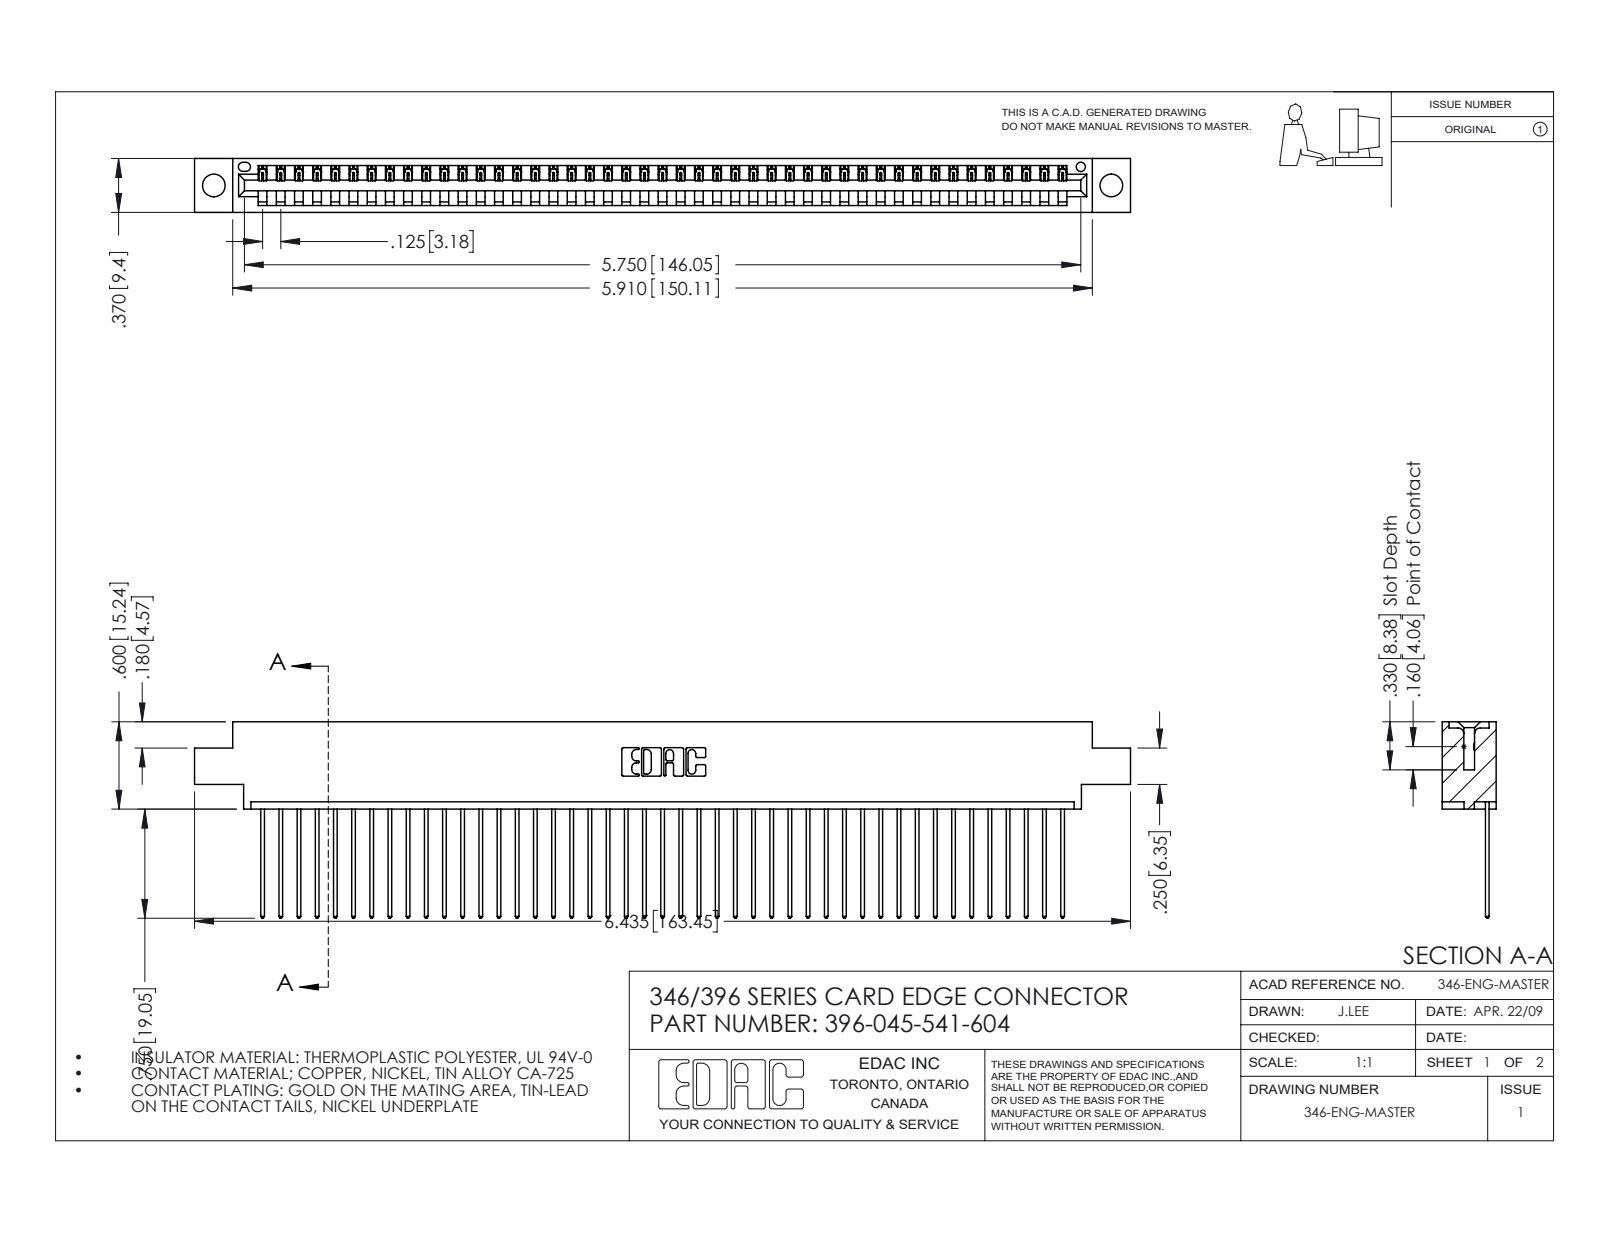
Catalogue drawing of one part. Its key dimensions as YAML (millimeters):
part_name: "345-292-001_345-293-141; 396-045-541-604; 346 Part_0.170 Offset - 0.156 Dia-TH"
step_written_by: "SolidWorks 2016 (CONFIG_CONTROL_DESIGN)"
units: millimeters
bodies: {solids: 46, faces: 2736, planar: 1880, cylindrical: 856, other: 0}
overall_size: [163.4, 34.3, 9.4]
volume: 15600
surface_area: 20350
round_holes:
  - {diameter: 4, count: 2}
  - {diameter: 1.6, count: 1}
partial_cylinders:
  - {radius: 0.2, count: 90}
  - {radius: 0.3, count: 90}
  - {radius: 0.3, count: 22}
  - {radius: 0.2, count: 6}
  - {radius: 0.8, count: 6}
  - {radius: 0.7, count: 3}
  - {radius: 0.8, count: 2}
  - {radius: 1, count: 2}
face_to_face_distances: [1.2, 8.2, 9.4, 6.4, 1.8, 7.6, 0.6, 3.8, 5.6, 2.5]
hole_center_spacings: [6.2, 151.4, 156.7]
